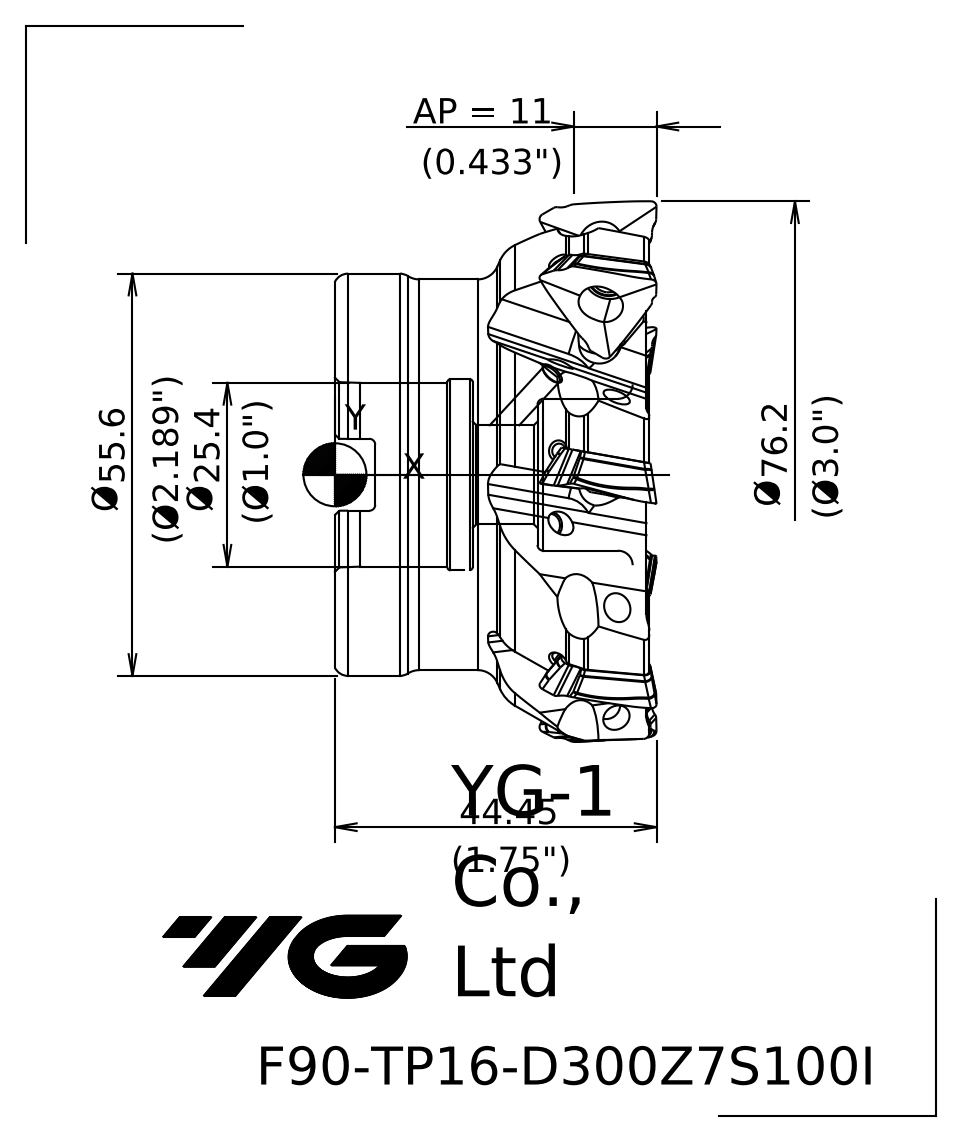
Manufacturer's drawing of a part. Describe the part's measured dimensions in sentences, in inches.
The part is named "1022C79461C3qzk0". Its 3-D file was written by "SIEMENS PLM Software NX 10.0 (AP203_CONFIGURATION_CONTROLLED_3D_DESIGN_OF_MECHANICAL_PARTS_AND_ASSEMBLIES_MIM_LF)". It is 2 solids with 314 faces: 23 planar, 11 cylindrical and 280 other. Overall it measures 3.005 by 3.005 by 1.75 inches. Its volume is 6.955 cubic inches and its surface area 44.78 square inches. Round holes: 1 of diameter 0.205, 1 of diameter 0.539, 1 of diameter 0.827, 1 of diameter 1, 1 of diameter 1.039. Round bosses or shafts: 1 of diameter 2.189, 1 of diameter 2.126. Partial cylindrical surfaces (rounded edges, fillets, slot ends): 2 of radius 0.031. The main face-to-face distances are 1.695, 0.945, 0.75, 1.476, 0.531, 0.219, 0.075, 0.87, 1.401, 1.62.
